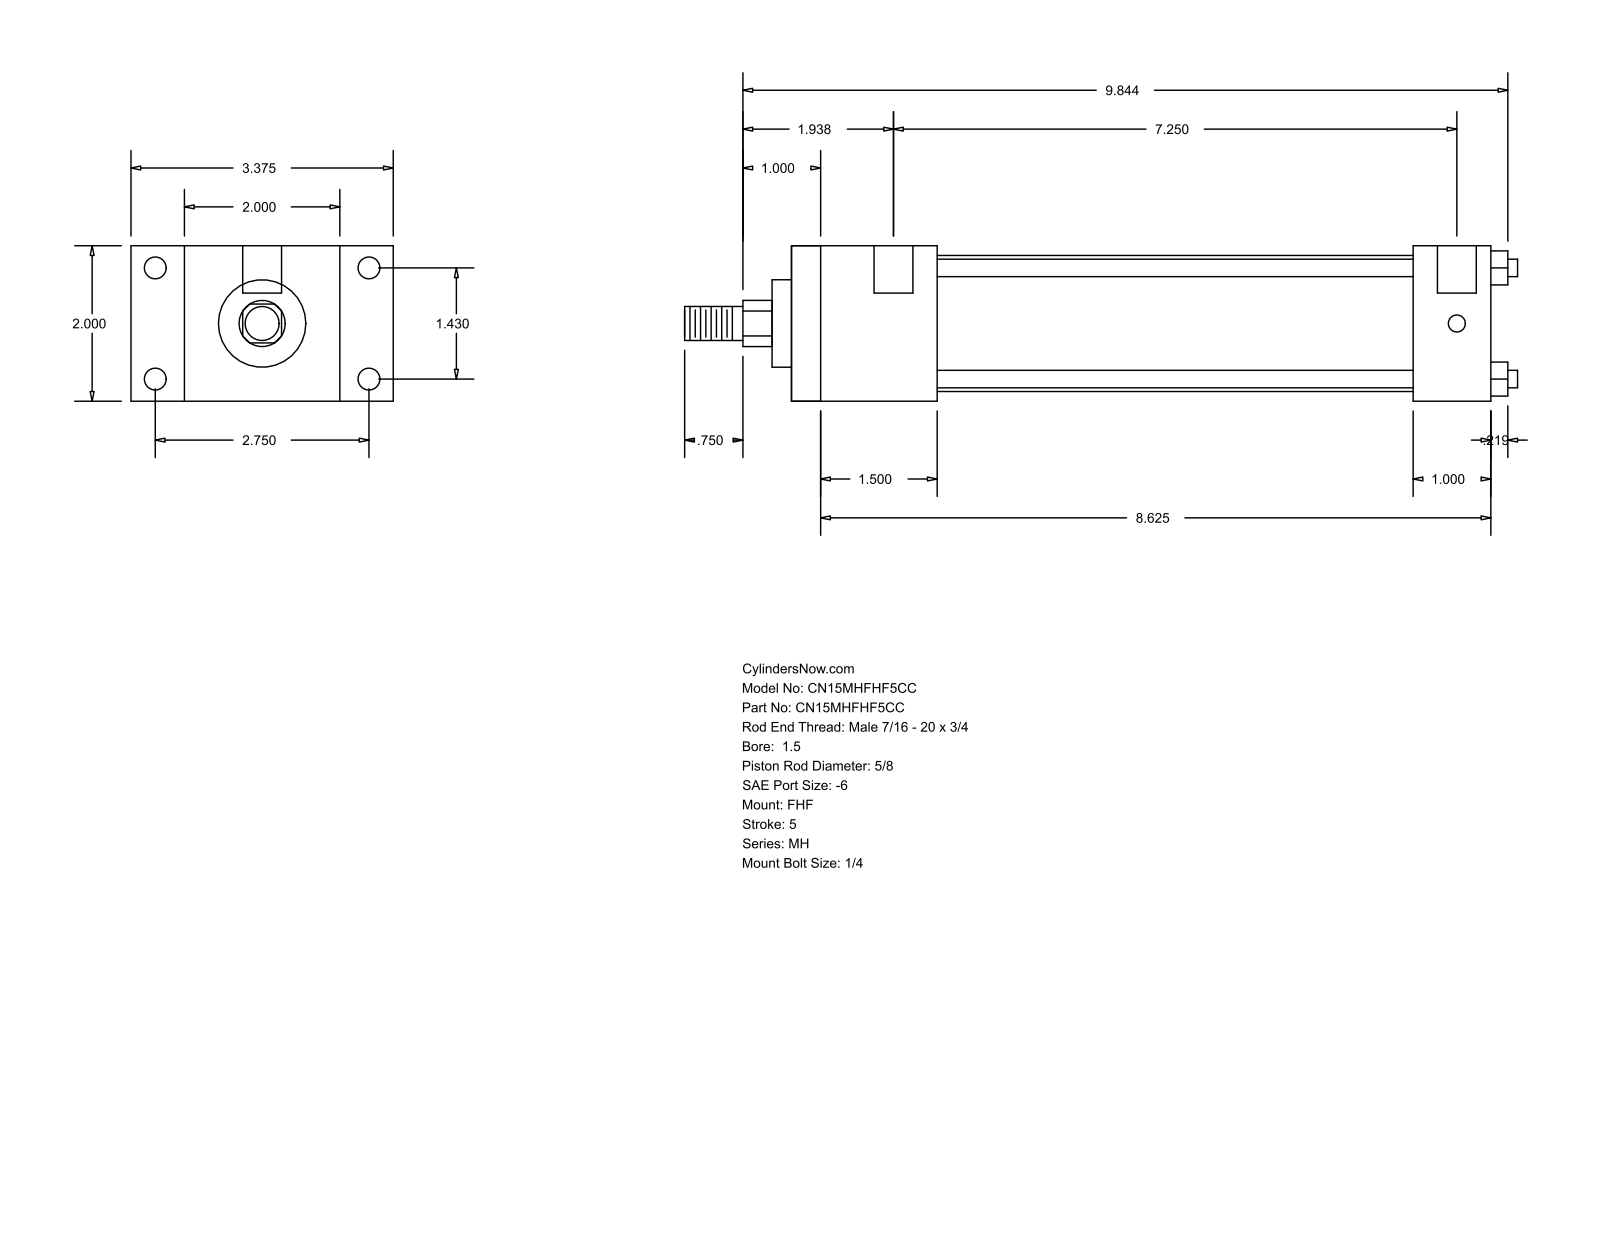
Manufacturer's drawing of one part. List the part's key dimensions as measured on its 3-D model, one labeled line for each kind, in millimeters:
Part name (STEP PRODUCT): MH_FHF__0150_0.625
STEP written by: GSSL Pune (CONFIG_CONTROL_DESIGN)
Units: millimetres
Bodies: 0 solids, 88 faces (60 planar, 28 cylindrical, 0 other)
Overall size (bounding box): 272.26 × 85.72 × 50.8
Round holes (diameter × count): ⌀5.56 ×4, ⌀7.14 ×4, ⌀12.7 ×2
Round bosses / shafts (diameter × count): ⌀5.71 ×4, ⌀44.45 ×1, ⌀28.57 ×1, ⌀15.88 ×1, ⌀11.11 ×1
Partial cylindrical surfaces — rounded edges, fillets, slot ends (radius × count): R7.54 ×1
Main face-to-face distances: 50.8, 17.46, 68.26, 47.62, 85.72, 228.59, 180.97, 25.4, 203.19, 155.57
Hole centre spacings: 36.32, 69.84, 78.72, 187.32, 3.17, 184.15
